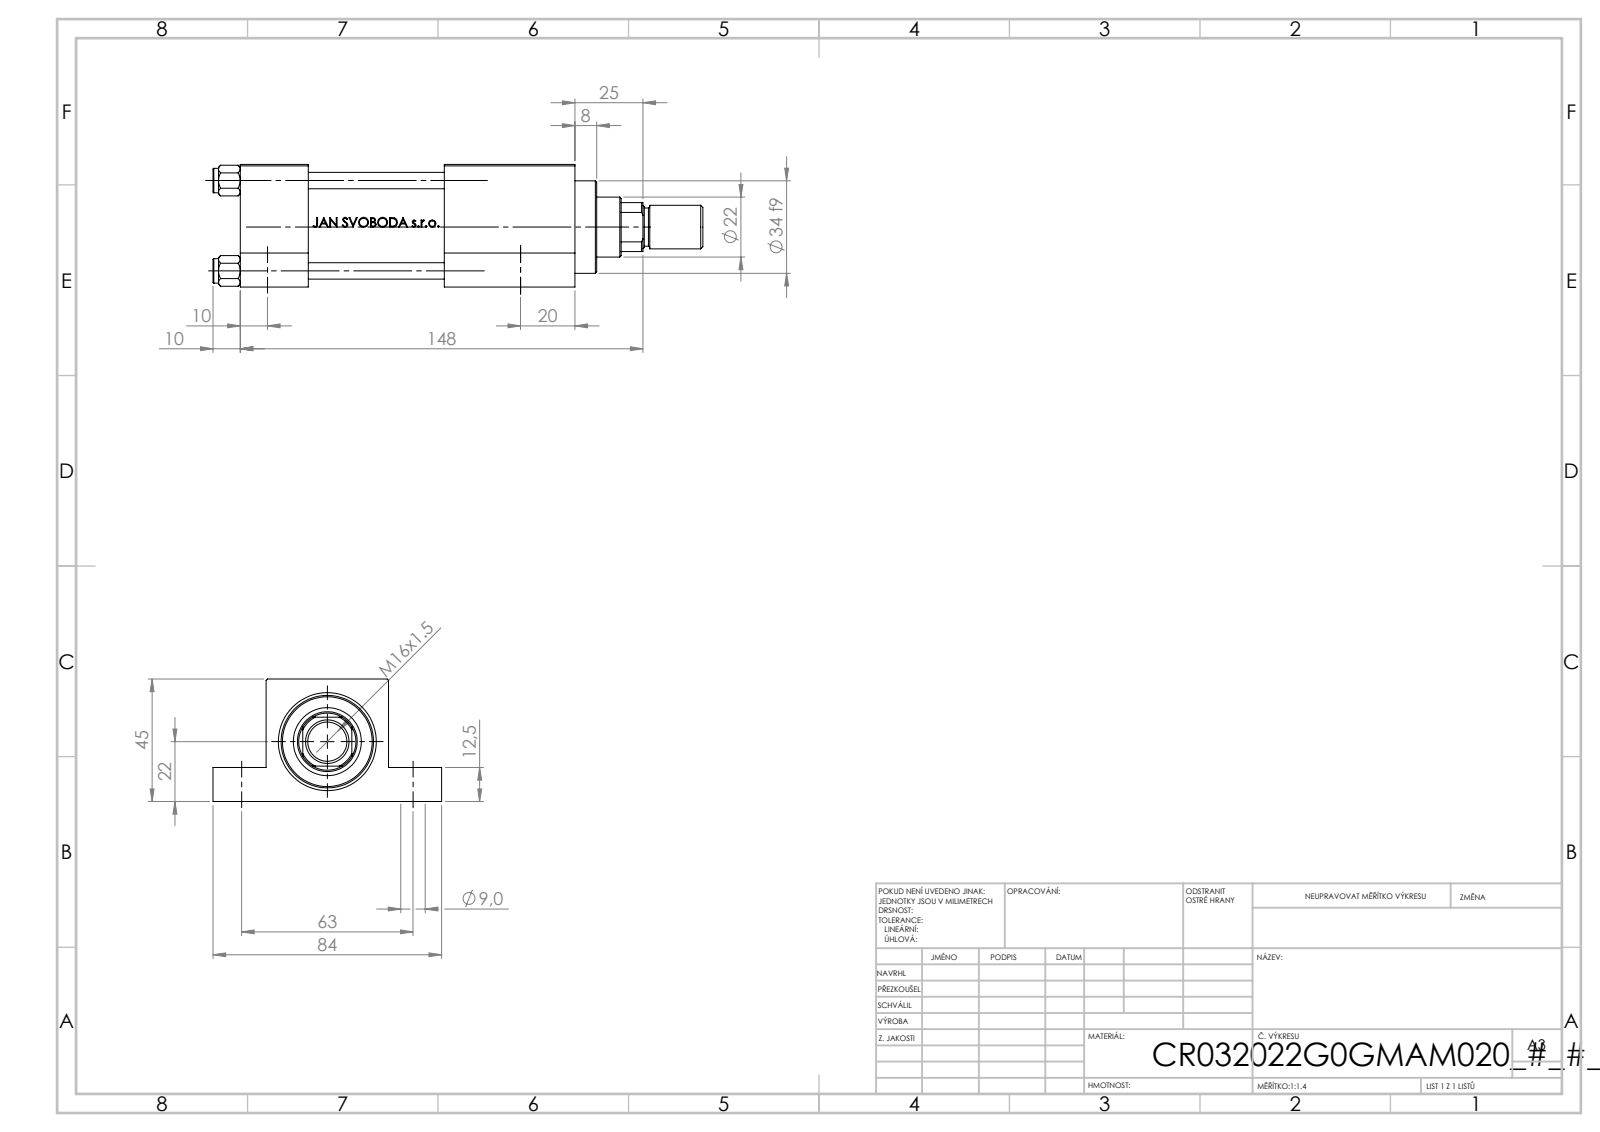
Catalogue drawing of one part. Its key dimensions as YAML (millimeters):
part_name: "NUT_M5_G; V215CR_G_Body; V215CR_VCP_G; V215CR_G_TYCINKA (+2 more)"
step_written_by: "SolidWorks 2019 (CONFIG_CONTROL_DESIGN)"
units: millimeters
bodies: {solids: 12, faces: 1100, planar: 434, cylindrical: 128, other: 538}
overall_size: [180, 84, 45]
volume: 248227
surface_area: 80219
round_holes:
  - {diameter: 6, count: 4}
  - {diameter: 9, count: 4}
  - {diameter: 7, count: 2}
  - {diameter: 13.16, count: 2}
  - {diameter: 20, count: 2}
  - {diameter: 10.5, count: 1}
  - {diameter: 22, count: 1}
  - {diameter: 24, count: 1}
  - {diameter: 25, count: 1}
  - {diameter: 32, count: 1}
  - {diameter: 33, count: 1}
round_bosses_or_shafts:
  - {diameter: 9, count: 4}
  - {diameter: 38, count: 1}
  - {diameter: 34, count: 1}
  - {diameter: 16, count: 1}
  - {diameter: 14, count: 1}
partial_cylinders:
  - {radius: 10.5, count: 1}
face_to_face_distances: [45, 25, 12.5, 32.5, 123, 19.5, 64.5, 98, 50, 75]
hole_center_spacings: [33.2, 23.13, 23.83, 46.95, 63, 93, 112.33, 75.5]
